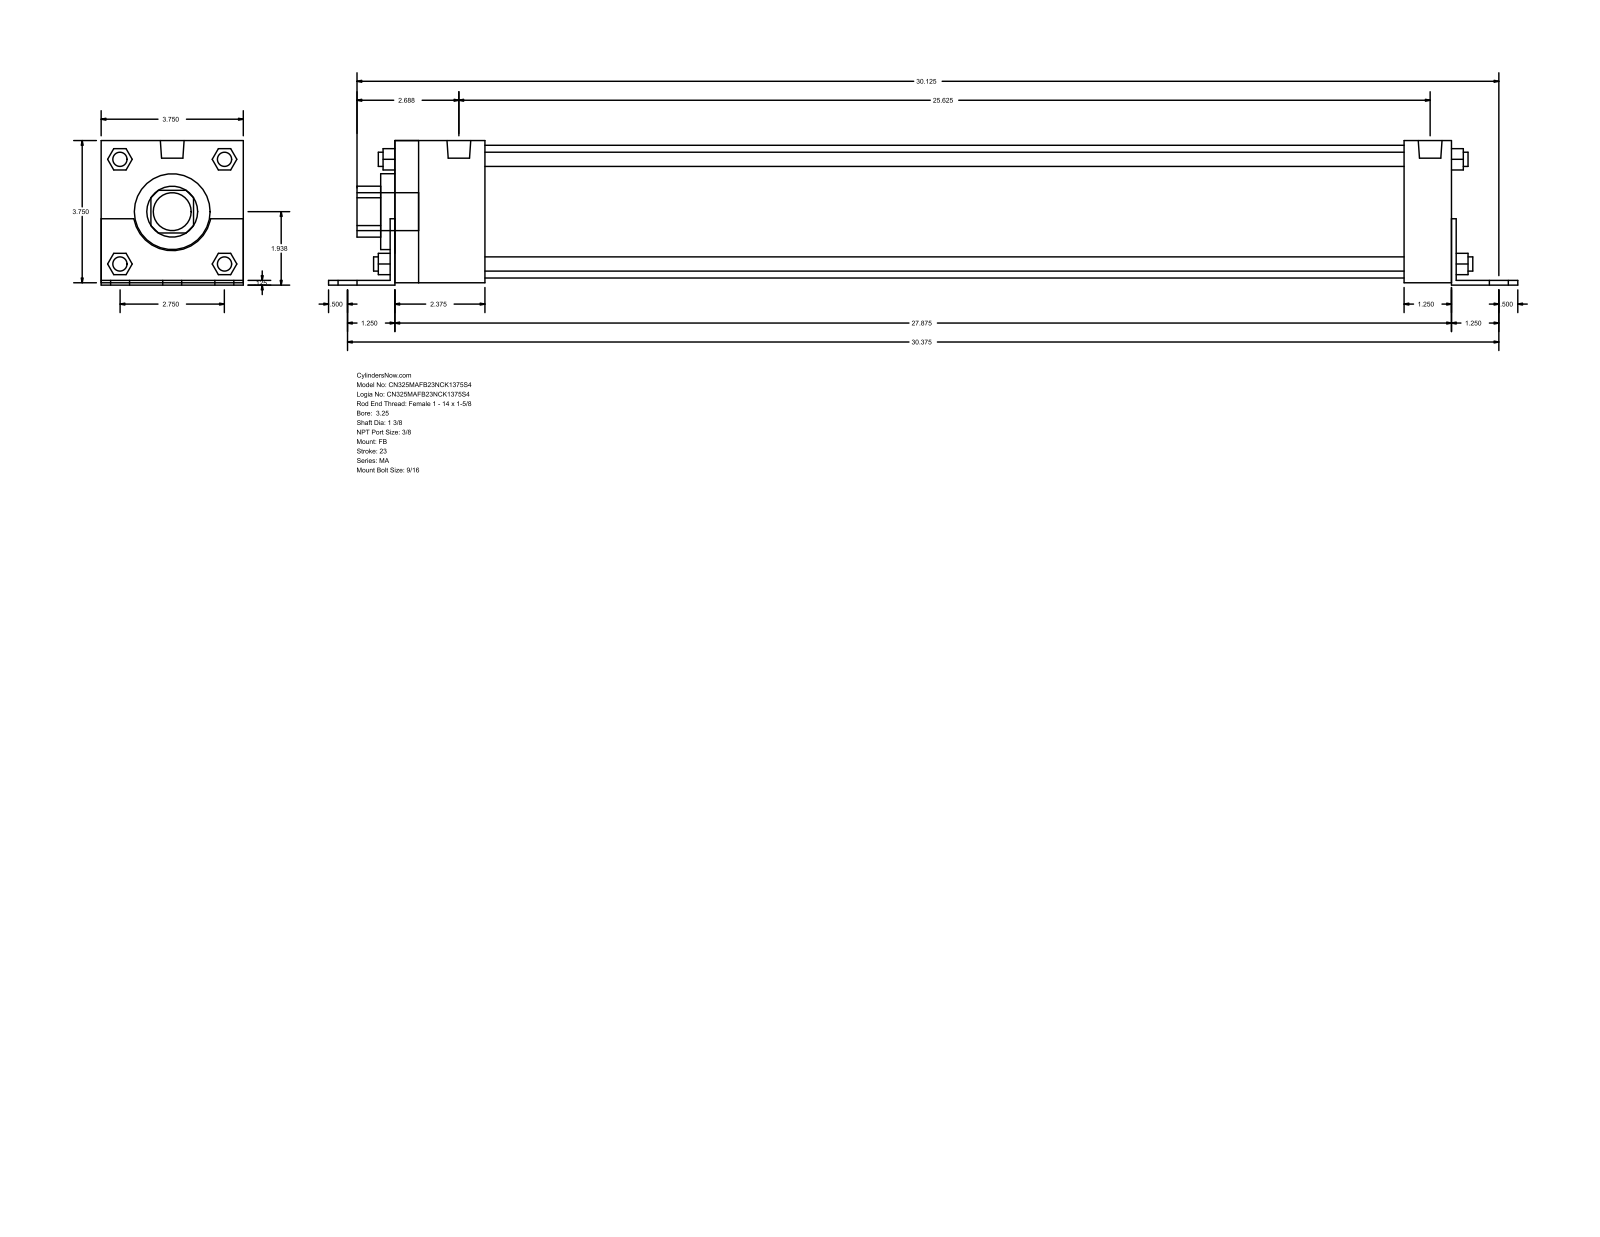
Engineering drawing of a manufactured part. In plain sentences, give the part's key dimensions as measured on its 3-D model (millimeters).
The part is named "MA_FB__0325_1.375". Its 3-D file was written by "GSSL Pune (CONFIG_CONTROL_DESIGN)". It is 0 solids with 140 faces: 105 planar, 35 cylindrical and 0 other. Overall it measures 796.92 by 96.84 by 95.25 millimeters. Round holes: 1 of diameter 34.92, 1 of diameter 50.8, 1 of diameter 88.9. Round bosses or shafts: 6 of diameter 14.29, 4 of diameter 11.11, 4 of diameter 9.53, 2 of diameter 15.93, 1 of diameter 25.4. Partial cylindrical surfaces (rounded edges, fillets, slot ends): 1 of radius 17.06, 1 of radius 26.16. The main face-to-face distances are 95.24, 3.17, 1.59, 96.83, 1.58, 93.66, 3.18, 708.02, 711.2, 31.75.
